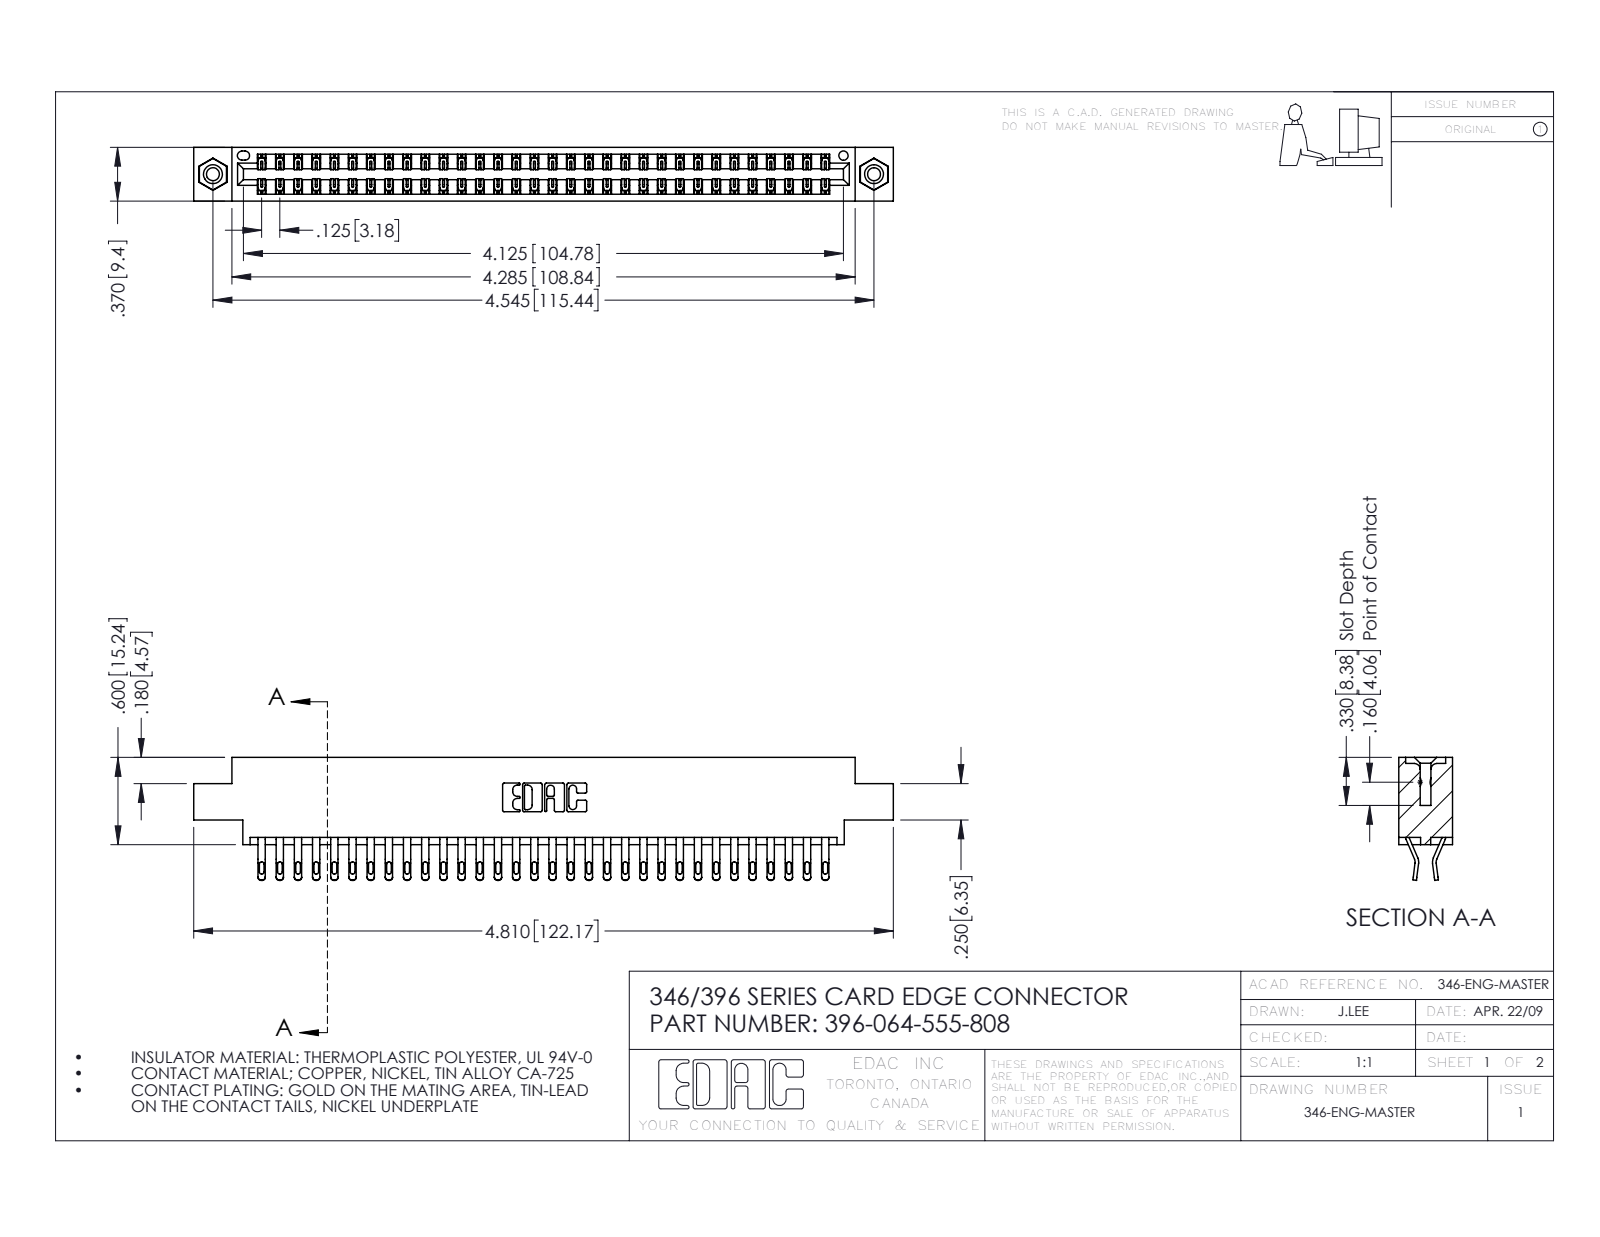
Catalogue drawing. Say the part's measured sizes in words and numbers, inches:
The part is named "346 Part_0.170 Offset - 0.156 Dia-TI; 345-292-001_555 Tail; 345-250-001_345-250-003-102; 396-064-555-808". Its 3-D file was written by "SolidWorks 2016 (CONFIG_CONTROL_DESIGN)". It is 67 solids with 3898 faces: 2224 planar, 1658 cylindrical and 16 other. Overall it measures 4.81 by 0.845 by 0.37 inches. Its volume is 0.724 cubic inches and its surface area 26.36 square inches. Round holes: 2 of diameter 0.089, 2 of diameter 0.125, 2 of diameter 0.156, 1 of diameter 0.064. Round bosses or shafts: 2 of diameter 0.155. Partial cylindrical surfaces (rounded edges, fillets, slot ends): 128 of radius 0.016, 128 of radius 0.02, 96 of radius 0.006, 22 of radius 0.01, 6 of radius 0.007, 6 of radius 0.031, 3 of radius 0.026, 2 of radius 0.01. The main face-to-face distances are 0.048, 0.322, 0.37, 0.25, 0.025, 0.072, 0.298, 0.275, 0.222, 0.148. The hole center spacings are 0.246, 4.337, 4.545.
